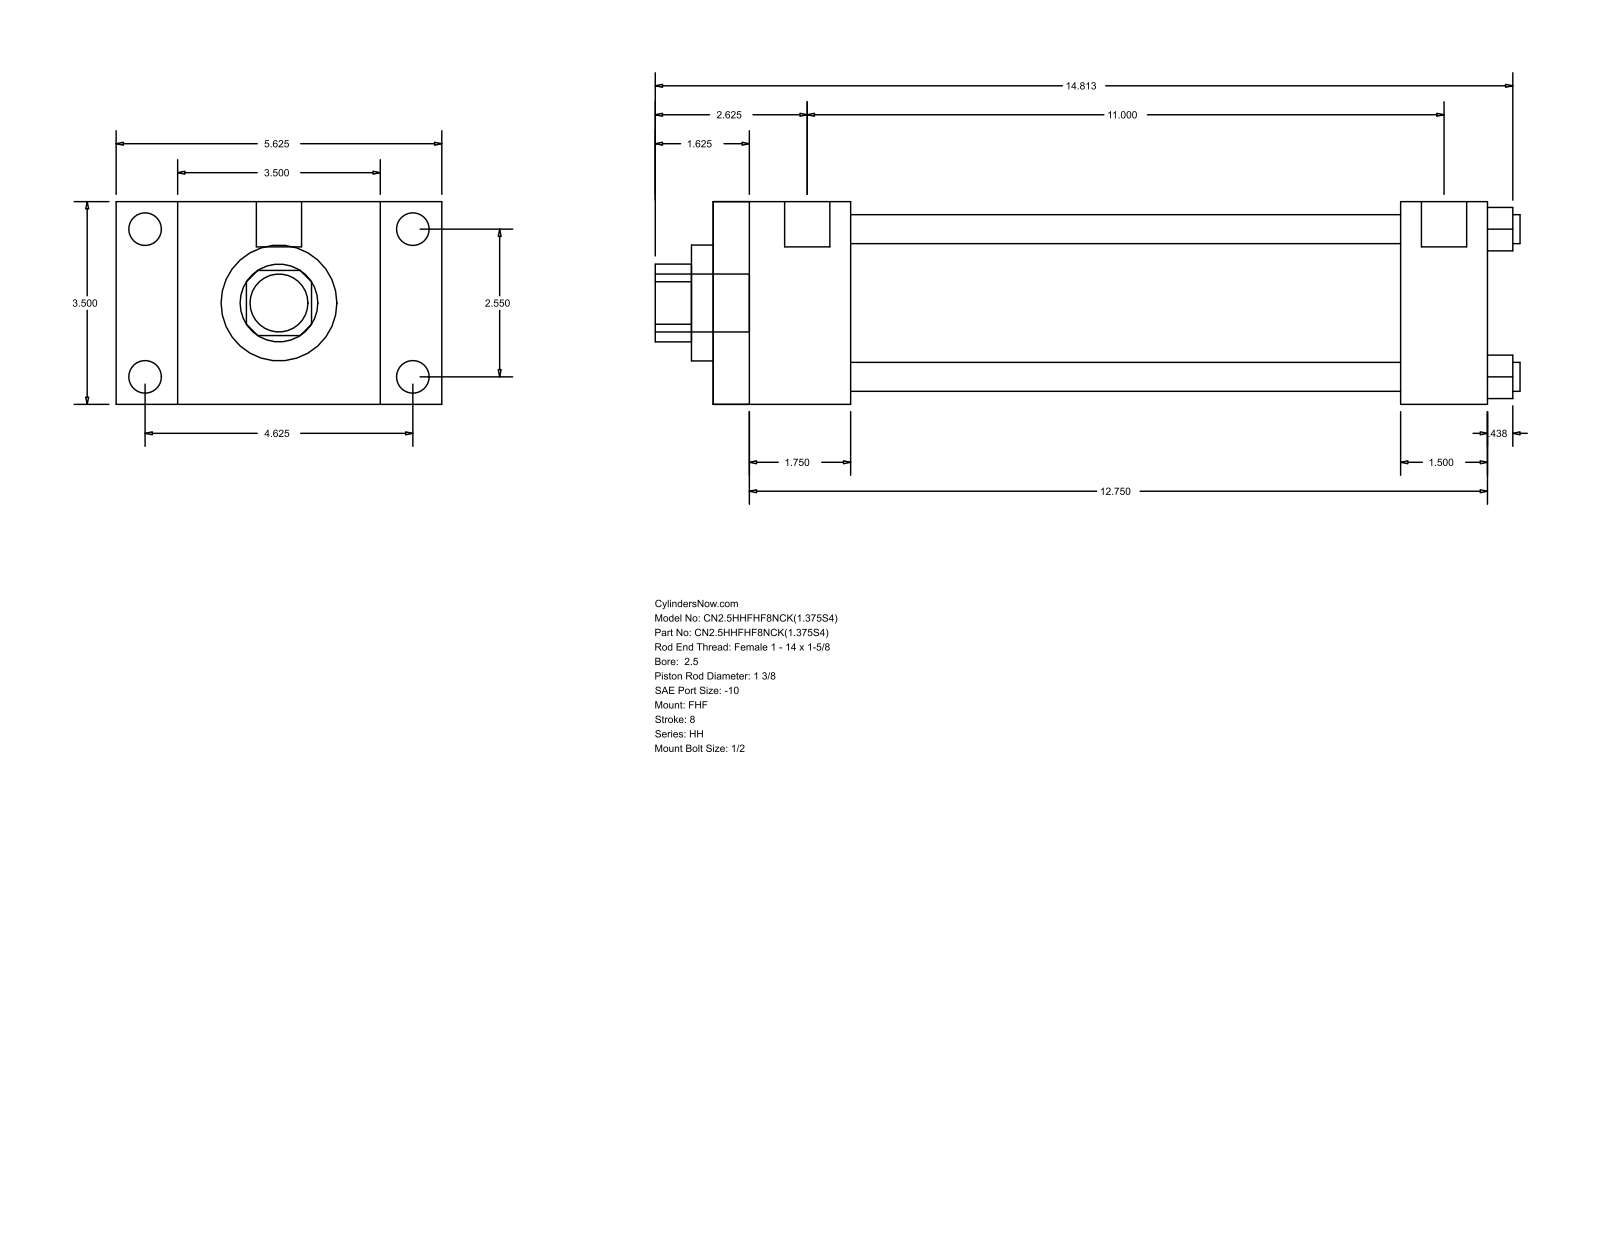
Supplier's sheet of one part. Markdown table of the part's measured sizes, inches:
| quantity | value |
| --- | --- |
| part name | HH_FHF__0250_1.375 |
| STEP written by | GSSL Pune (CONFIG_CONTROL_DESIGN) |
| units | inches |
| bodies | 0 solids, 88 faces (60 planar, 28 cylindrical, 0 other) |
| overall size | 14.937 × 5.625 × 3.5 |
| round holes (diameter × count) | 0.5 × 4, 1.375 × 1, 2 × 1, 2.875 × 1 |
| round bosses / shafts (diameter × count) | 0.563 × 4, 0.219 × 4, 0.781 × 2, 1 × 1 |
| partial cylindrical surfaces (radius × count) | 0.672 × 1 |
| main face-to-face distances | 3.5, 2.375, 1.063, 4.563, 13.375, 11, 5.625, 11.875, 9.5, 1.5 |
| hole center spacings | 1.803, 2.55, 3.606 |
